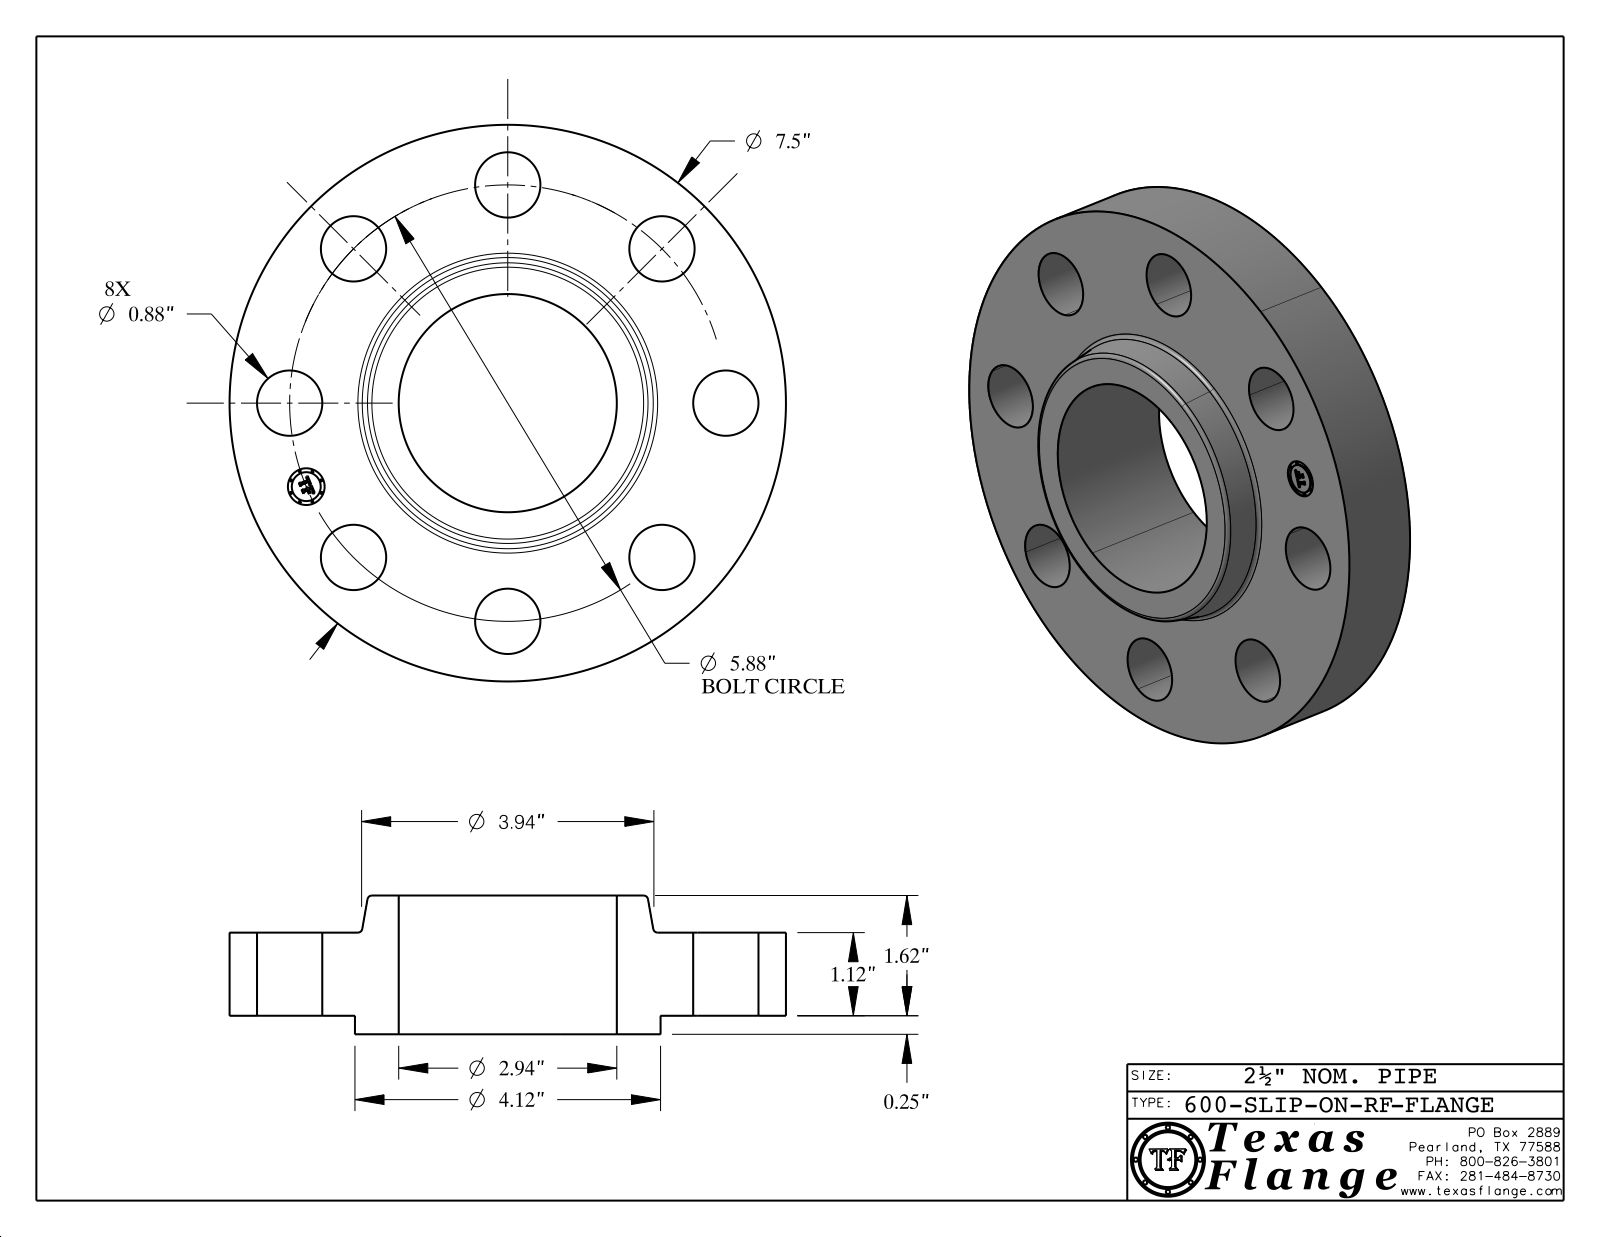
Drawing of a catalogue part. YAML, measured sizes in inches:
part_name: "600-SLIP-ON-RF"
step_written_by: "CATIA V5 STEP AP214 (AUTOMOTIVE_DESIGN)"
units: inches
bodies: {solids: 1, faces: 417, planar: 369, cylindrical: 42, other: 6}
overall_size: [7.5, 7.5, 1.87]
volume: 40.5
surface_area: 141.5
round_holes:
  - {diameter: 0.88, count: 8}
  - {diameter: 0.495, count: 1}
  - {diameter: 2.94, count: 1}
round_bosses_or_shafts:
  - {diameter: 0.03, count: 8}
  - {diameter: 7.5, count: 1}
  - {diameter: 4.12, count: 1}
  - {diameter: 0.39, count: 1}
face_to_face_distances: [1.12, 0.25, 1.37, 1.87, 1.62, 0.5, 0.015, 1.355, 1.105, 0.515]
hole_center_spacings: [2.25, 5.432, 2.94, 2.94, 4.157, 4.158, 3.267, 5.88]
